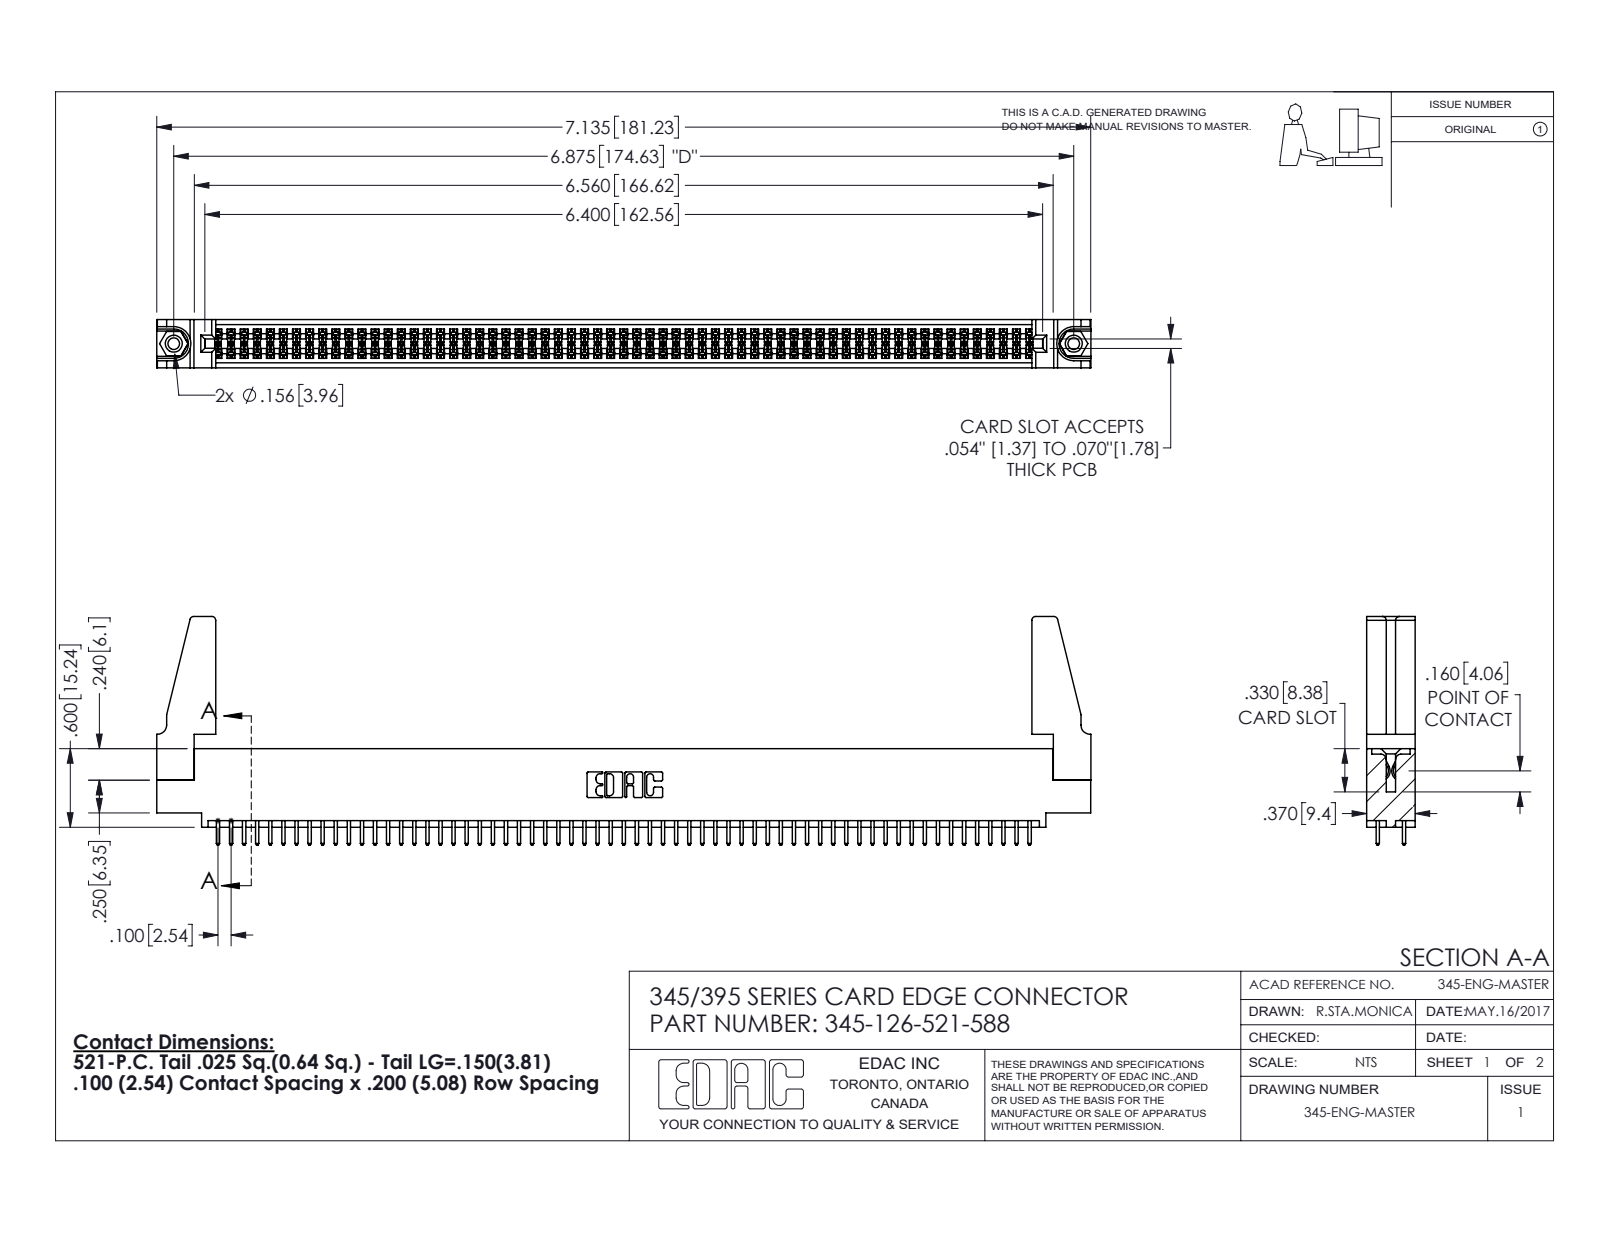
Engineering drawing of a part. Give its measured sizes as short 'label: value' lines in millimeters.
name: 345 Part_0.110 Offset - 0.156 Dia-TH; 345-126-521-588; 345-292-001_345-293-121; 345-220-078_345-220-088 (+1 more)
written by: SolidWorks 2016 (CONFIG_CONTROL_DESIGN)
unit: mm
bodies: 131 solids, 6554 faces (4314 planar, 2224 cylindrical, 16 other)
size: 181.3 × 44.4 × 9.4
volume: 20 930 mm³; area: 29 420 mm²
holes: 2× ⌀2.3, 2× ⌀3.2, 2× ⌀4, 1× ⌀1.6
bosses: 2× ⌀3.9
rounds: 189× R0.2, 126× R0.3, 22× R0.3, 8× R0.8, 6× R0.2, 6× R0.8, 3× R0.7, 2× R0.4
face distances: 1.8, 7.6, 9.4, 5.1, 2.5, 6.9, 0.6, 5.7, 4.4, 3.8
hole spacings: 6.9, 168.6, 174.6
